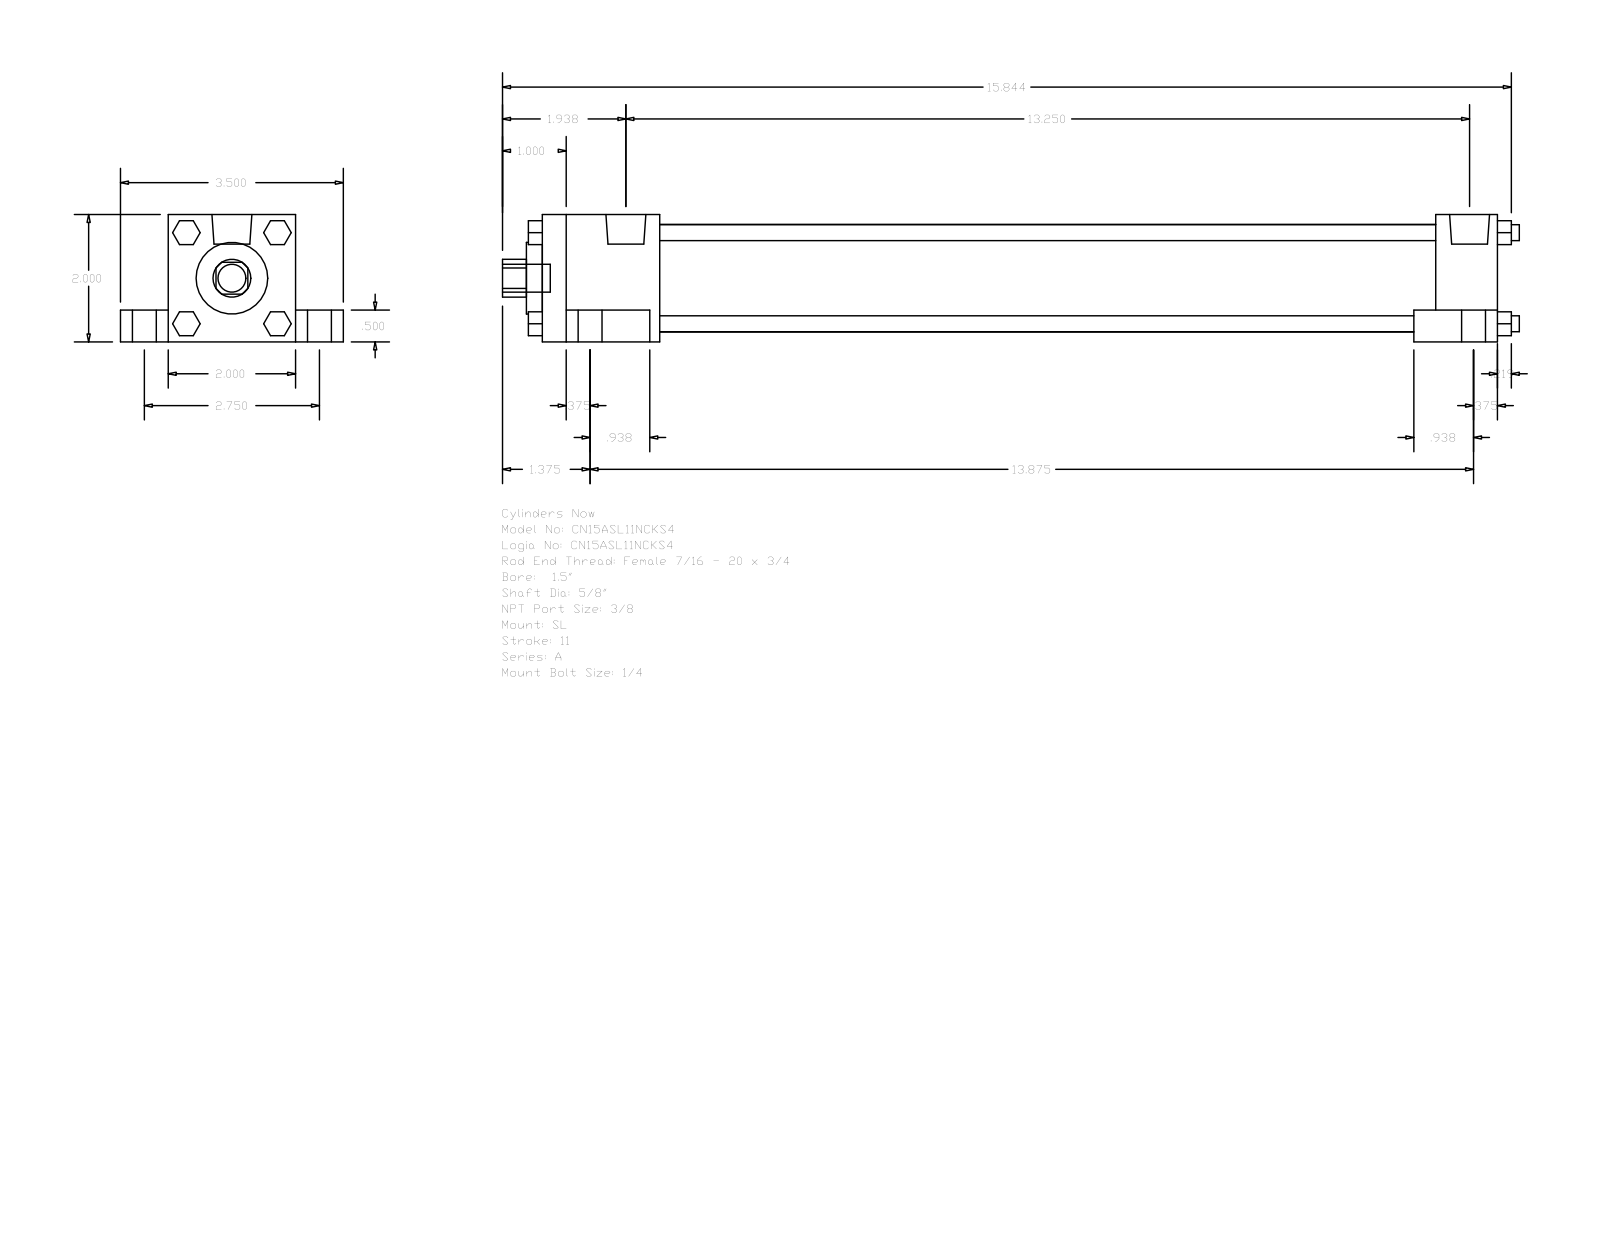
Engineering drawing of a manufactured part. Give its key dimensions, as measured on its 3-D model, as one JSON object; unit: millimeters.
{"part_name": "A_SL__0150_0.625", "step_written_by": "GSSL Pune (CONFIG_CONTROL_DESIGN)", "units": "millimeters", "bodies": {"solids": 0, "faces": 148, "planar": 112, "cylindrical": 36, "other": 0}, "overall_size": [405.61, 88.9, 50.8], "round_holes": [[15.88, 1], [28.57, 1], [42.93, 1]], "round_bosses_or_shafts": [[15.88, 4], [9.53, 4], [6.35, 4], [5.56, 4], [15.93, 2], [11.11, 1]], "partial_cylinders_radius": [[7.54, 1]], "face_to_face_distances": [50.8, 19.05, 12.7, 38.1, 69.85, 381, 9.52, 33.34, 356.39, 24.61]}
